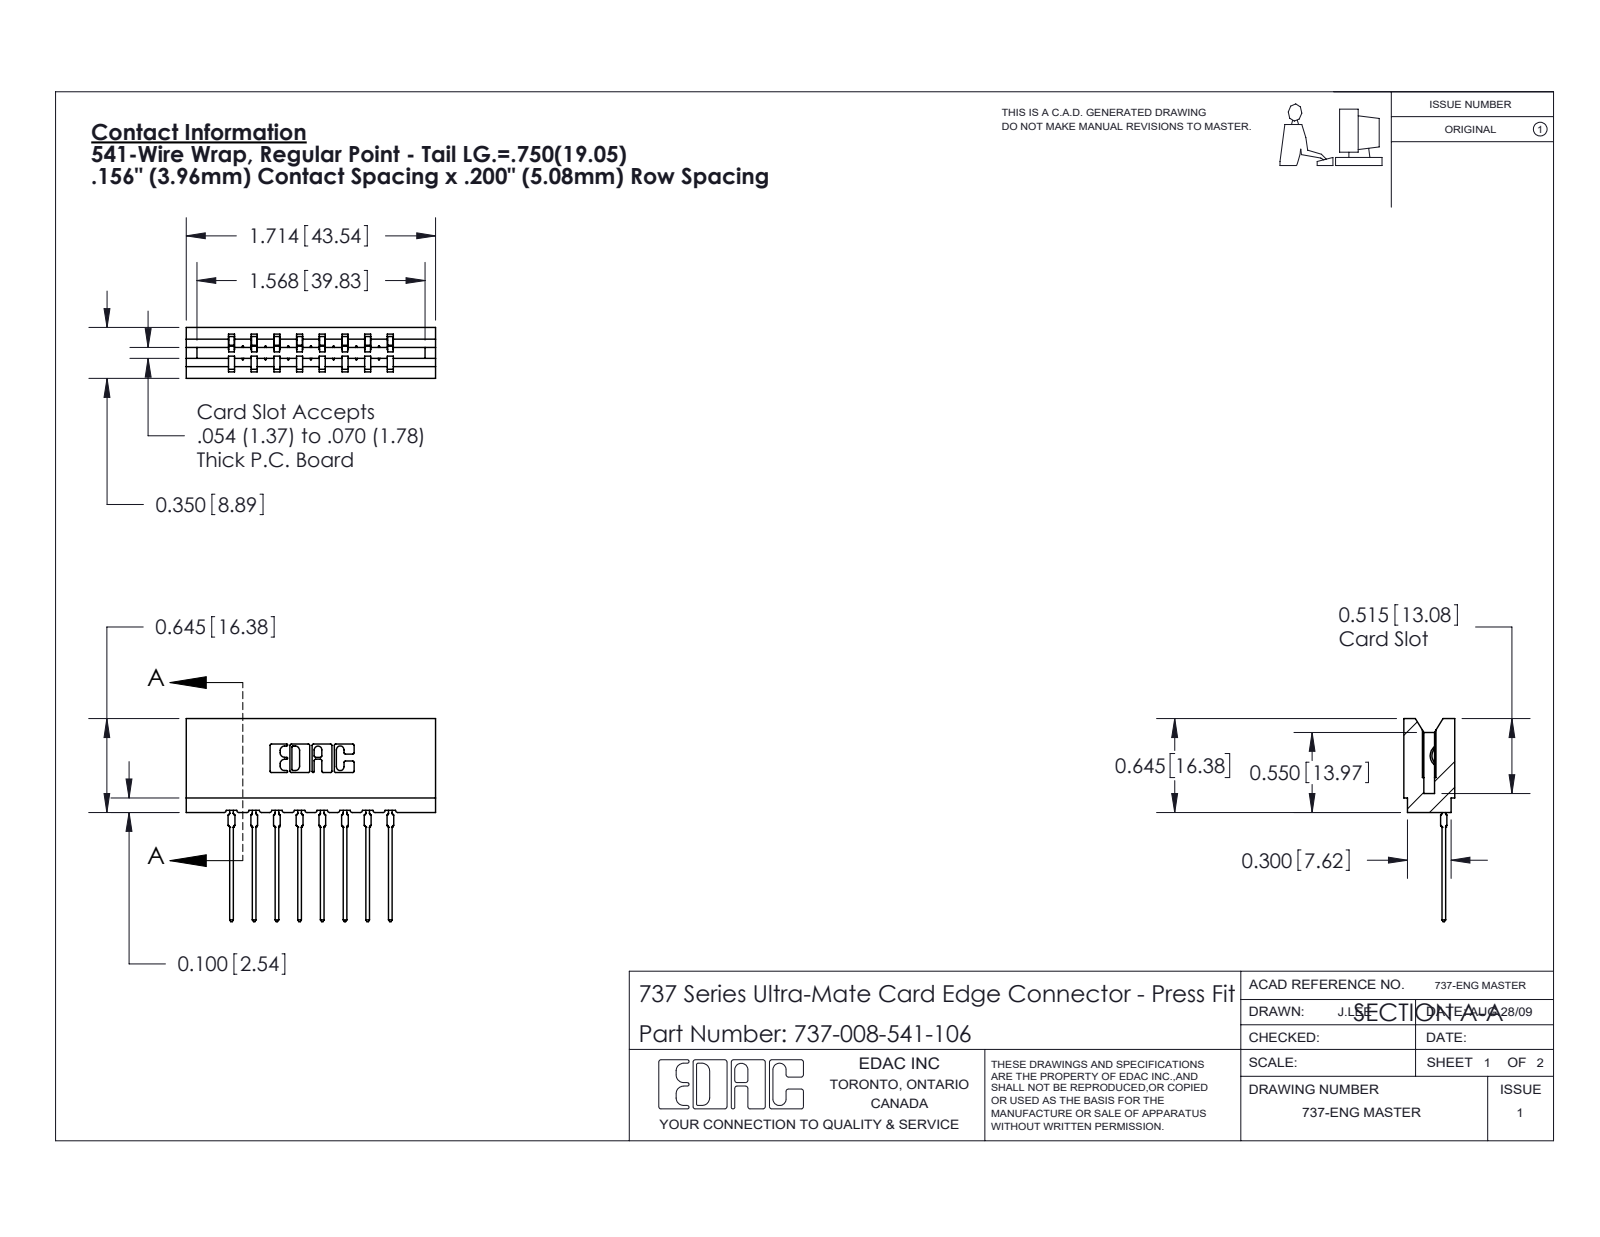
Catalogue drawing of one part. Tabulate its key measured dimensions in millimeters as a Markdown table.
| quantity | value |
| --- | --- |
| part name | 737-008-541-106; 737 Part_Insulator Option - 06; 745-292-001_541 |
| STEP written by | SolidWorks 2020 (CONFIG_CONTROL_DESIGN) |
| units | millimeters |
| bodies | 9 solids, 999 faces (599 planar, 192 cylindrical, 208 other) |
| overall size | 43.5 × 35.5 × 8.9 |
| volume | 4 460 mm³ |
| surface area | 5 543 mm² |
| partial cylindrical surfaces (radius × count) | 0.3 × 22, 0.4 × 16, 0.5 × 16, 0.2 × 6, 0.8 × 6, 0.1 × 4, 0.3 × 4, 0.7 × 3 |
| main face-to-face distances | 4, 3.5, 5.4, 8.9, 7.9, 15.8, 9, 11.9, 19.8, 5 |
